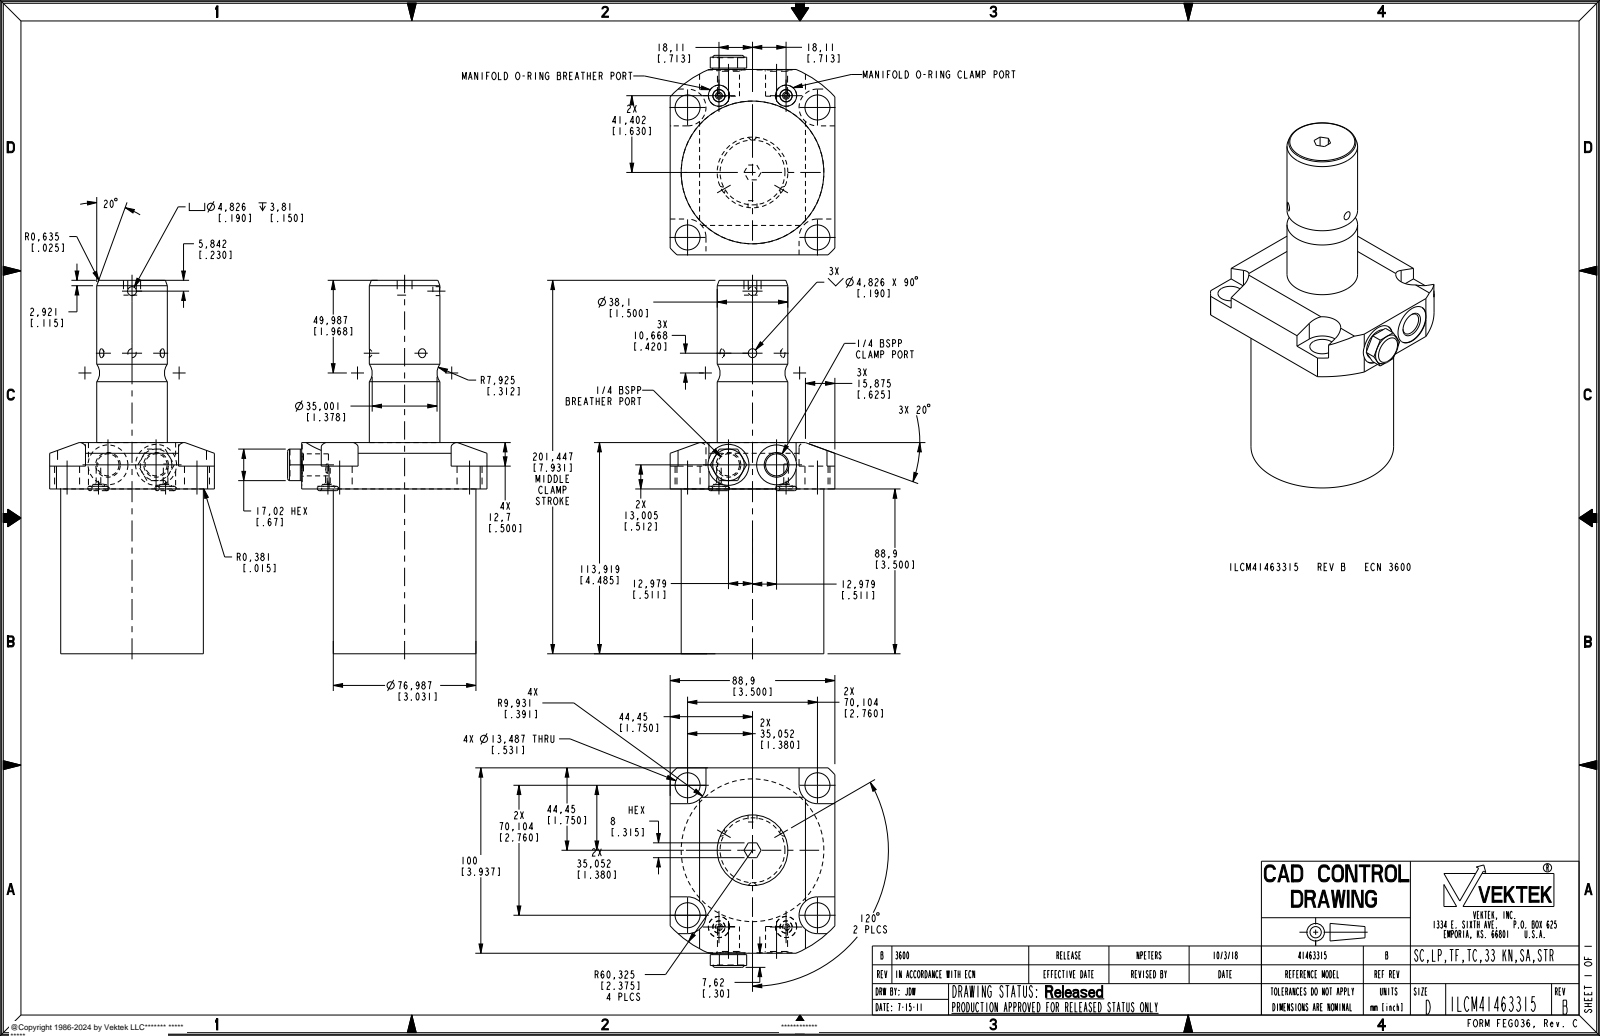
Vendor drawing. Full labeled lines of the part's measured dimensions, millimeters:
Part name (STEP PRODUCT): ILCM41463315
STEP written by: PRO/ENGINEER BY PARAMETRIC TECHNOLOGY CORPORATION, 2013320 (AUTOMOTIVE_DESIGN)
Units: millimetres
Bodies: 3 solids, 143 faces (63 planar, 48 cylindrical, 32 other)
Overall size (bounding box): 201.45 × 107.62 × 88.9
Volume: 694 259 mm³ · Surface area: 61 129 mm²
Round holes (diameter × count): ⌀13.49 ×4, ⌀2.49 ×2, ⌀6.5 ×2, ⌀11.4 ×2, ⌀11.89 ×2, ⌀4.83 ×1, ⌀17.02 ×1, ⌀21.49 ×1, ⌀22.1 ×1
Round bosses / shafts (diameter × count): ⌀76.99 ×1, ⌀38.1 ×1
Partial cylindrical surfaces — rounded edges, fillets, slot ends (radius × count): R9.93 ×4, R60.33 ×1
Main face-to-face distances: 88.9, 113.92, 25.02, 201.45, 112.55, 87.53, 101.22, 12.32, 12.7, 100.23
Hole centre spacings: 70.1, 18.09, 53.54, 78.3, 93.12, 94.58, 99.14, 25.96
